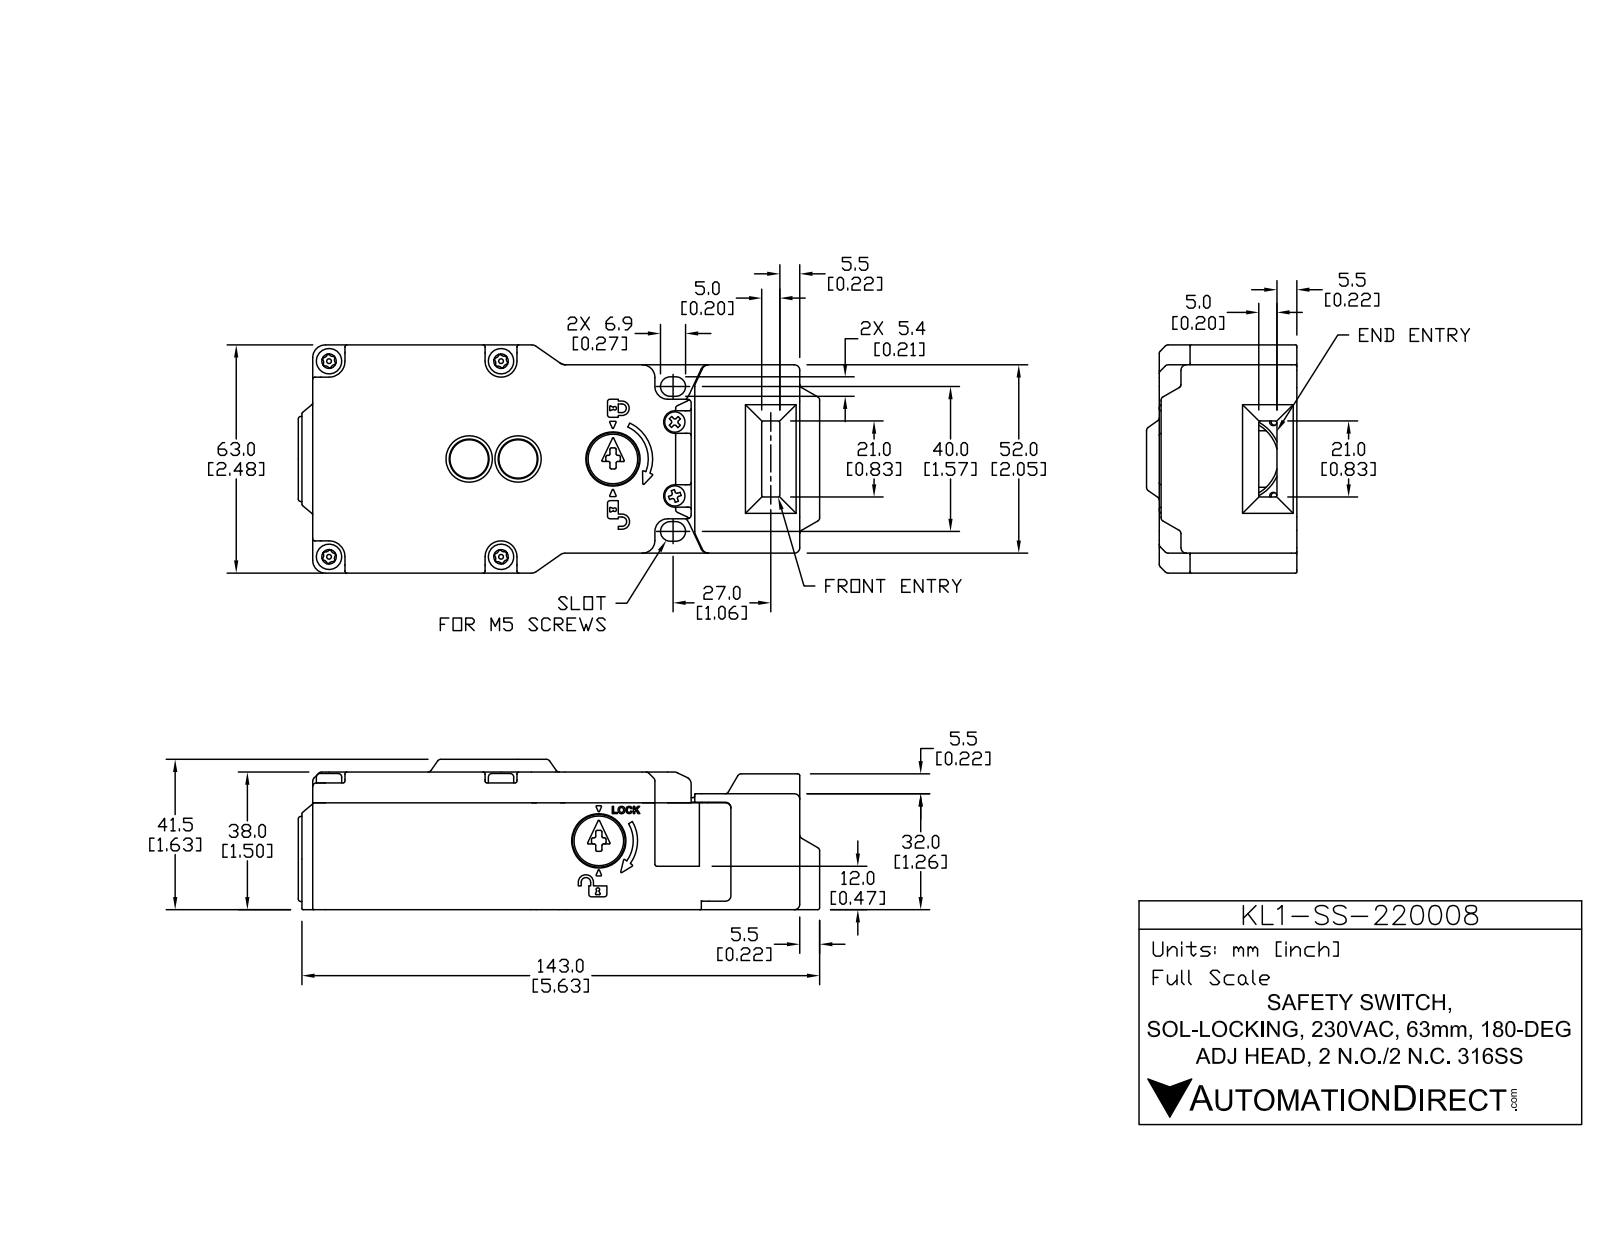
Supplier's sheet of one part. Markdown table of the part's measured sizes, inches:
| quantity | value |
| --- | --- |
| part name | KL1-SS-220008 |
| STEP written by | SolidWorks 2017 (AUTOMOTIVE_DESIGN) |
| units | inches |
| bodies | 18 solids, 3047 faces (909 planar, 1225 cylindrical, 913 other) |
| overall size | 5.669 × 2.48 × 1.634 |
| volume | 6.348 in³ |
| surface area | 118.8 in² |
| round holes (diameter × count) | 0.102 × 4, 0.134 × 4, 0.157 × 4, 0.161 × 4, 0.177 × 4, 0.197 × 4, 0.079 × 2, 0.083 × 2, 0.118 × 2, 0.126 × 2, 0.142 × 2, 0.264 × 2 |
| round bosses / shafts (diameter × count) | 0.276 × 4, 0.138 × 4, 0.051 × 4, 0.197 × 3, 0.039 × 3, 0.571 × 2, 0.417 × 2, 0.362 × 2 |
| partial cylindrical surfaces (radius × count) | 0.02 × 348, 0.012 × 126, 0.039 × 106, 0.008 × 30, 0.016 × 24, 0.059 × 16, 0.006 × 14, 0.028 × 12 |
| main face-to-face distances | 0.098, 0.118, 0.217, 1.496, 1.398, 1.402, 1.303, 0.094, 2.264, 2.146 |
| hole center spacings | 0.404, 0.498, 0.515, 0.549, 0.784, 0.803, 1.079, 1.118 |
